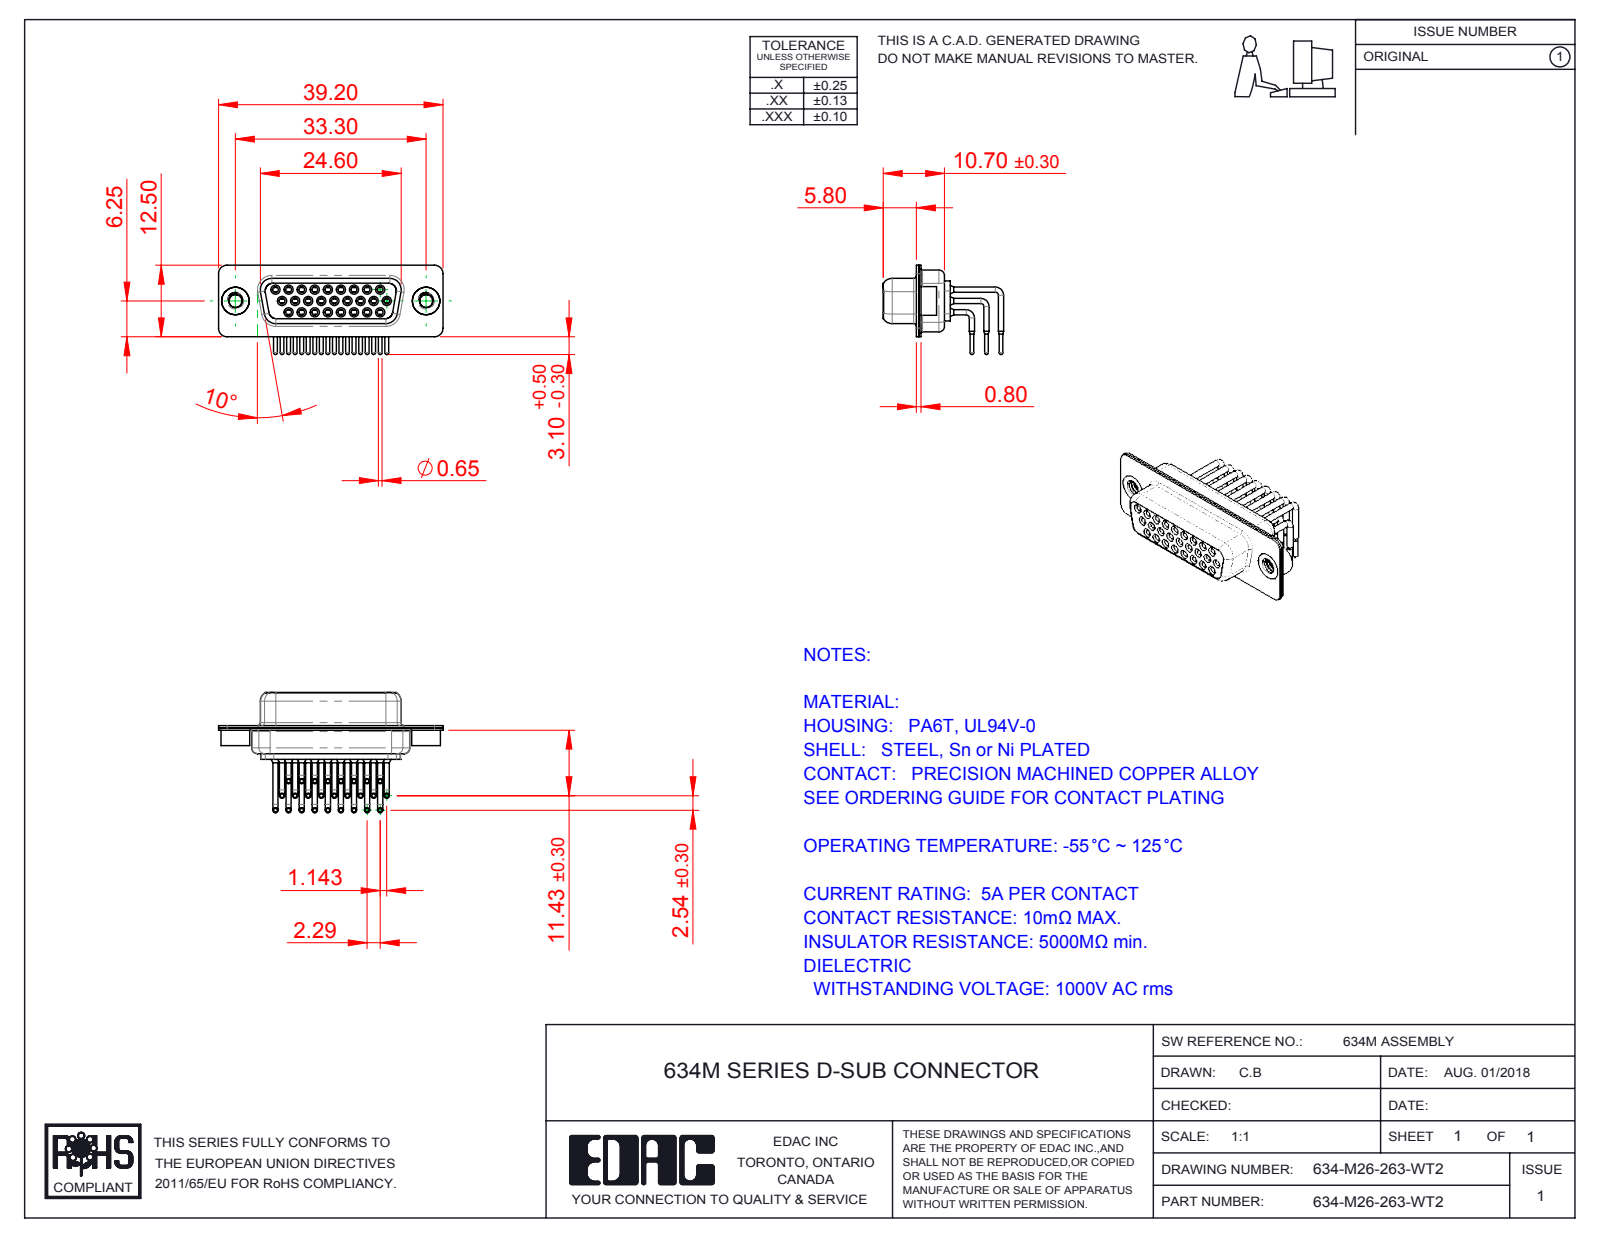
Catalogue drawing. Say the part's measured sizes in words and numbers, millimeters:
The part is named "634M Housing_26 Contacts; 634-M26-263-WT2; 634M Shell Rear_26 Contacts; 634M Contact Row 1 (+4 more)". Its 3-D file was written by "SolidWorks 2016 (CONFIG_CONTROL_DESIGN)". It is 31 solids with 1657 faces: 457 planar, 735 cylindrical and 465 other. Overall it measures 39.2 by 21.02 by 15.6 millimeters. Its volume is 2 533 cubic millimeters and its surface area 8 471 square millimeters. Round holes: 26 of diameter 1, 26 of diameter 1.1, 26 of diameter 1.7, 26 of diameter 1.8, 26 of diameter 2, 2 of diameter 2.26, 2 of diameter 4, 2 of diameter 4.8. Round bosses or shafts: 52 of diameter 0.9, 26 of diameter 1.6, 26 of diameter 1.5, 26 of diameter 0.65, 2 of diameter 5, 2 of diameter 4.9, 1 of diameter 2. Partial cylindrical surfaces (rounded edges, fillets, slot ends): 16 of radius 1.5, 12 of radius 2, 8 of radius 1.35, 8 of radius 1.6, 4 of radius 0.25, 4 of radius 0.5, 4 of radius 0.6, 4 of radius 0.65. The main face-to-face distances are 0.4, 2.3, 1.45, 8.95, 8.5, 1.9, 0.8, 6.2, 0.45, 7.05. The hole center spacings are 3.96, 2.28, 4.57, 6.05, 2.29, 8.24, 6.86, 6.04.
